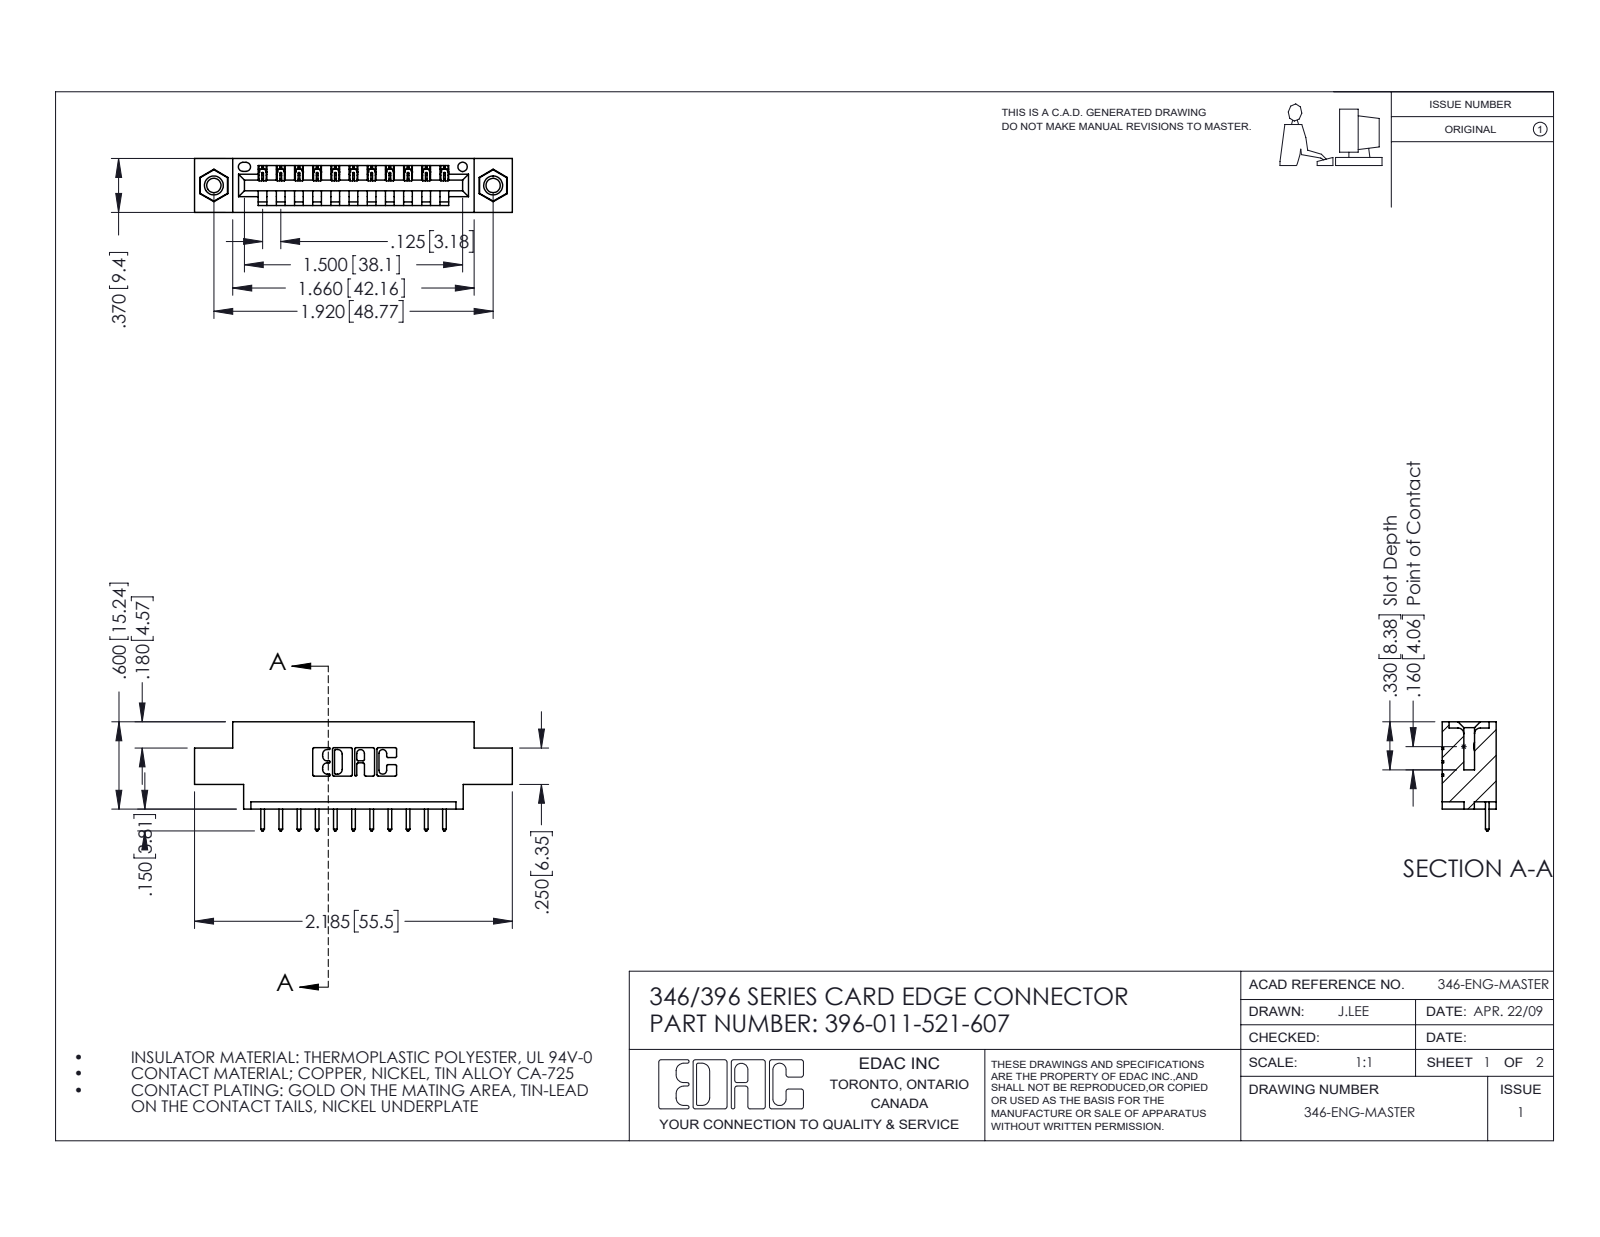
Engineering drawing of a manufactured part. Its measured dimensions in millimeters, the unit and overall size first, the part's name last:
Units: millimetres
Overall size (bounding box): 55.5 × 19.1 × 9.4
Round holes (diameter × count): ⌀2.5 ×2, ⌀3.2 ×2, ⌀4 ×2, ⌀1.6 ×1
Round bosses / shafts (diameter × count): ⌀3.9 ×2
Partial cylindrical surfaces — rounded edges, fillets, slot ends (radius × count): R0.2 ×22, R0.3 ×22, R0.3 ×22, R0.2 ×6, R0.8 ×6, R0.7 ×3, R0.8 ×2, R1 ×2
Main face-to-face distances: 6.4, 9.4, 1.2, 8.2, 5.6, 3.8, 2.5, 4.4, 1.8, 7.6
Hole centre spacings: 6.2, 43.6, 48.8
Volume: 4 900 mm³ · Surface area: 5 860 mm²
Bodies: 14 solids, 824 faces (552 planar, 256 cylindrical, 16 other)
Part name (STEP PRODUCT): 345-292-001_345-293-121; 345-250-001_345-250-005-103; 346 Part_0.170 Offset - 0.156 Dia-TI; 396-011-521-607
STEP written by: SolidWorks 2016 (CONFIG_CONTROL_DESIGN)
